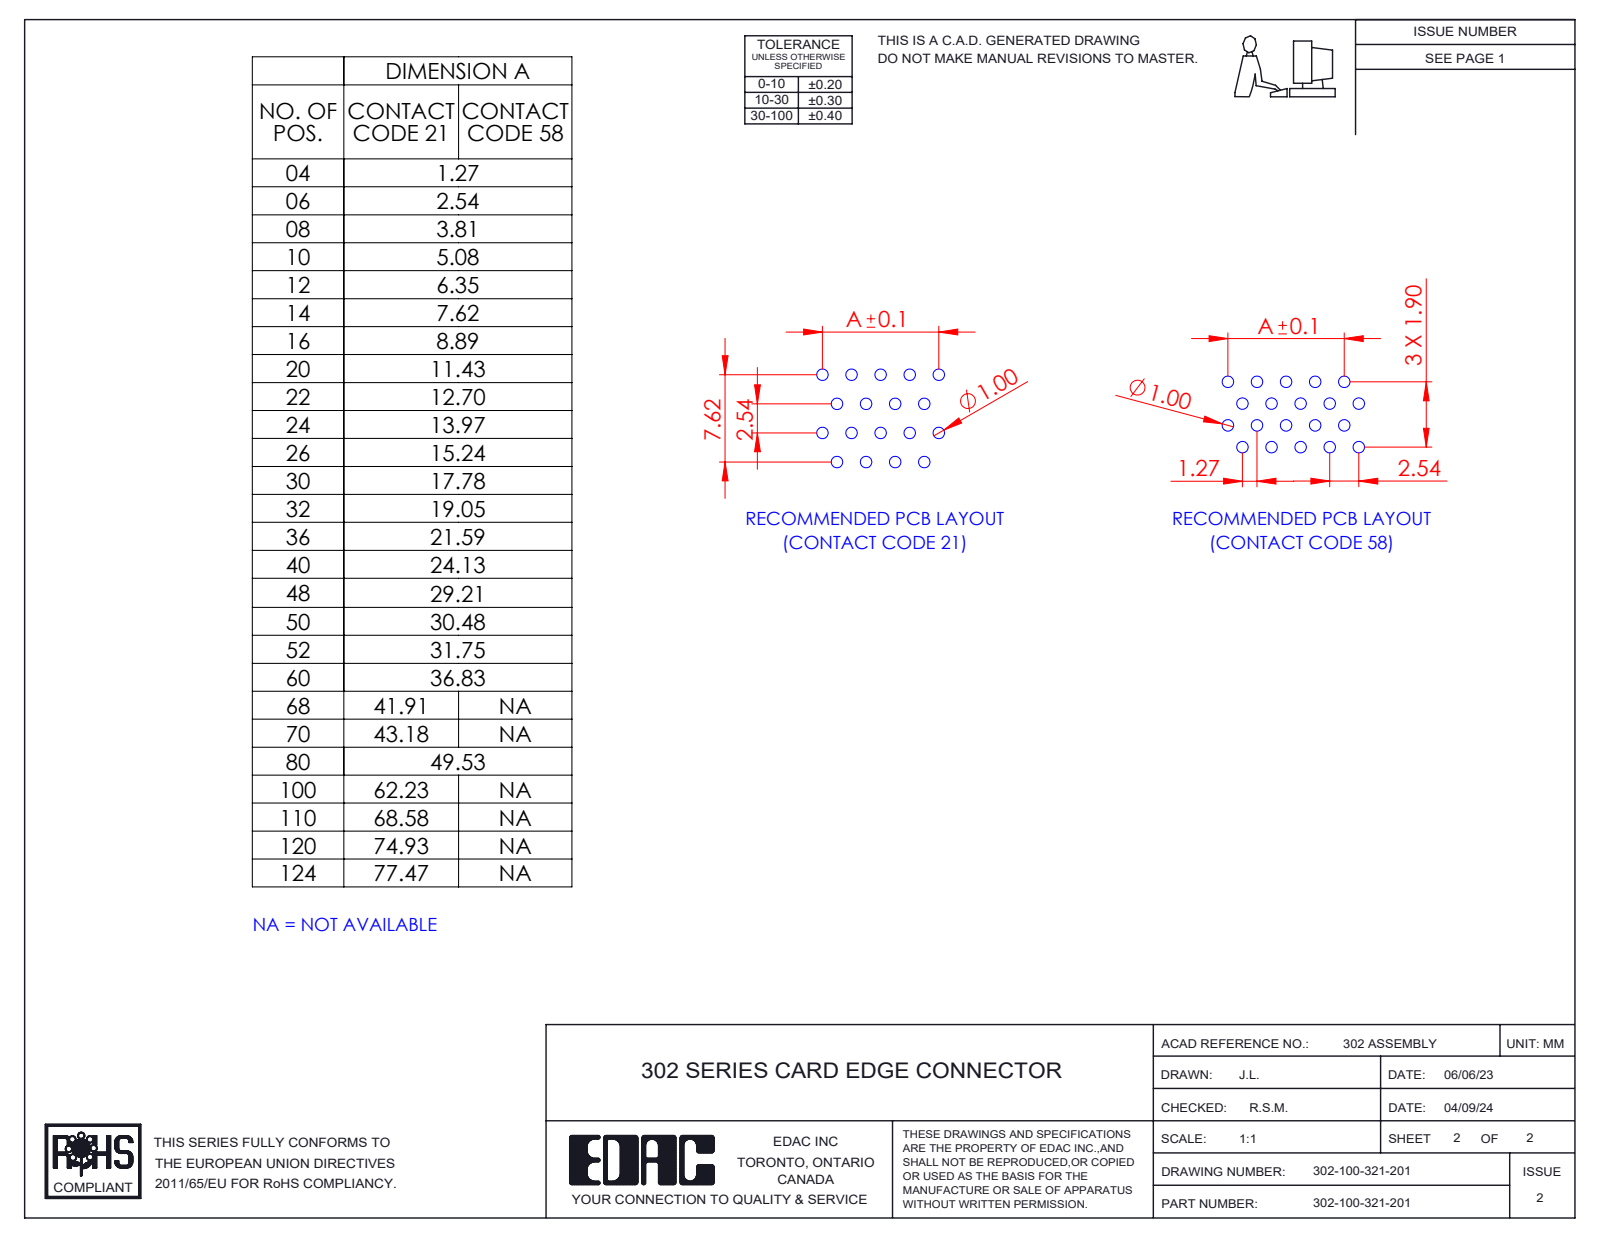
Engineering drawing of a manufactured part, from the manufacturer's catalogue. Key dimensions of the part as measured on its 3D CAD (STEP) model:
Part name (STEP PRODUCT): 302-100-321-201; HSG_Vertical HSG; Contact_302-290-X21 (2); Contact_302-290-X21 (1)
STEP written by: SolidWorks 2023 (CONFIG_CONTROL_DESIGN)
Units: millimetres
Bodies: 101 solids, 4616 faces (3399 planar, 1013 cylindrical, 204 other)
Overall size (bounding box): 69.6 × 17.63 × 8.88
Volume: 5 324 mm³ · Surface area: 15 070 mm²
Partial cylindrical surfaces — rounded edges, fillets, slot ends (radius × count): R0.2 ×108, R2.03 ×4, R2.09 ×4, R0.11 ×2, R0.4 ×2, R0.41 ×2, R1.25 ×2, R1.53 ×2
Main face-to-face distances: 8.88, 2.54, 1.27, 5.08, 3.81, 7.62, 6.35, 8.89, 10.16, 3.49
